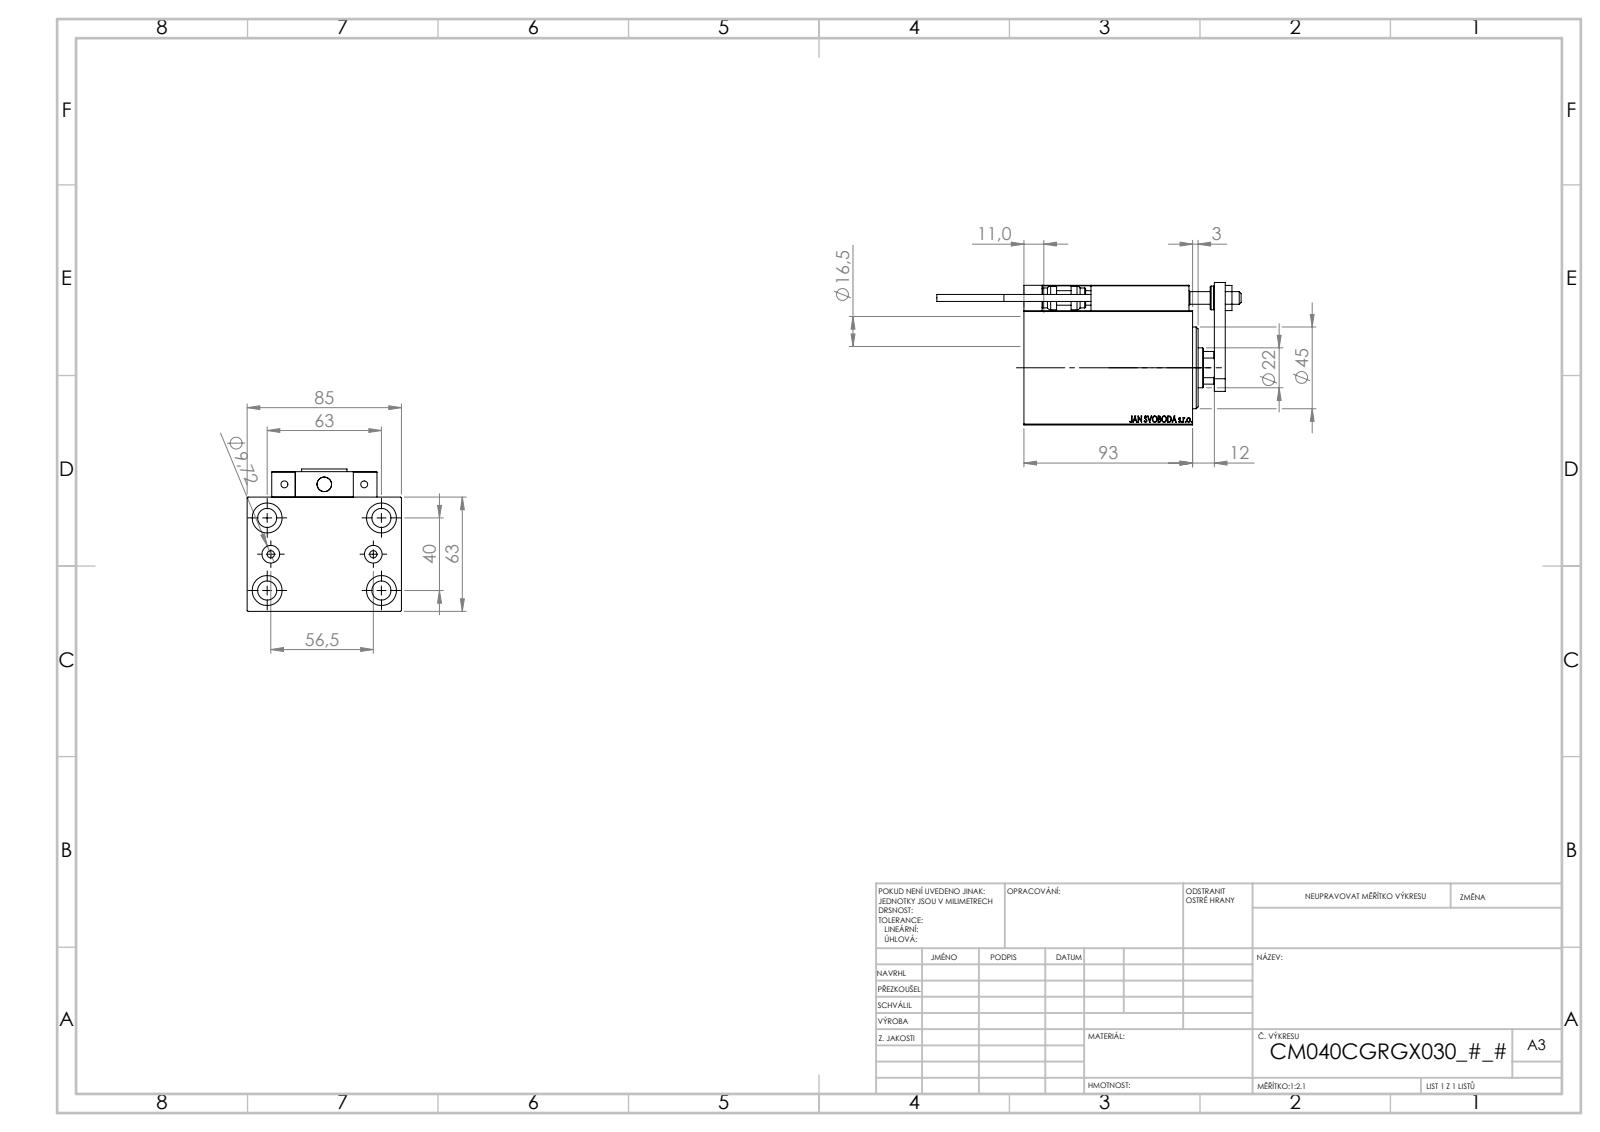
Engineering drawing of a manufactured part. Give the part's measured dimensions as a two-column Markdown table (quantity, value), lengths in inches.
| quantity | value |
| --- | --- |
| part name | Block; KONCOVKA; ALLEN BOLT D8; V450CM_C_Body (+7 more) |
| STEP written by | SolidWorks 2019 (CONFIG_CONTROL_DESIGN) |
| units | inches |
| bodies | 23 solids, 1278 faces (560 planar, 184 cylindrical, 534 other) |
| overall size | 6.602 × 3.346 × 3.091 |
| volume | 29.21 in³ |
| surface area | 164.9 in² |
| round holes (diameter × count) | 0.157 × 6, 0.315 × 5, 0.65 × 5, 0.126 × 4, 0.413 × 4, 0.197 × 2, 0.383 × 2, 0.276 × 1, 0.492 × 1, 0.866 × 1, 1.004 × 1, 1.575 × 1 |
| round bosses / shafts (diameter × count) | 0.197 × 2, 0.15 × 2, 0.512 × 1, 0.433 × 1 |
| partial cylindrical surfaces (radius × count) | 0.012 × 30, 0.118 × 2, 0.413 × 1 |
| main face-to-face distances | 2.48, 3.346, 0.472, 3.189, 3.661, 0.551, 1.181, 3.031, 1.772, 0.591 |
| hole center spacings | 1.469, 0.448, 0.787, 0.791, 0.807, 1.165, 1.169, 1.42 |
